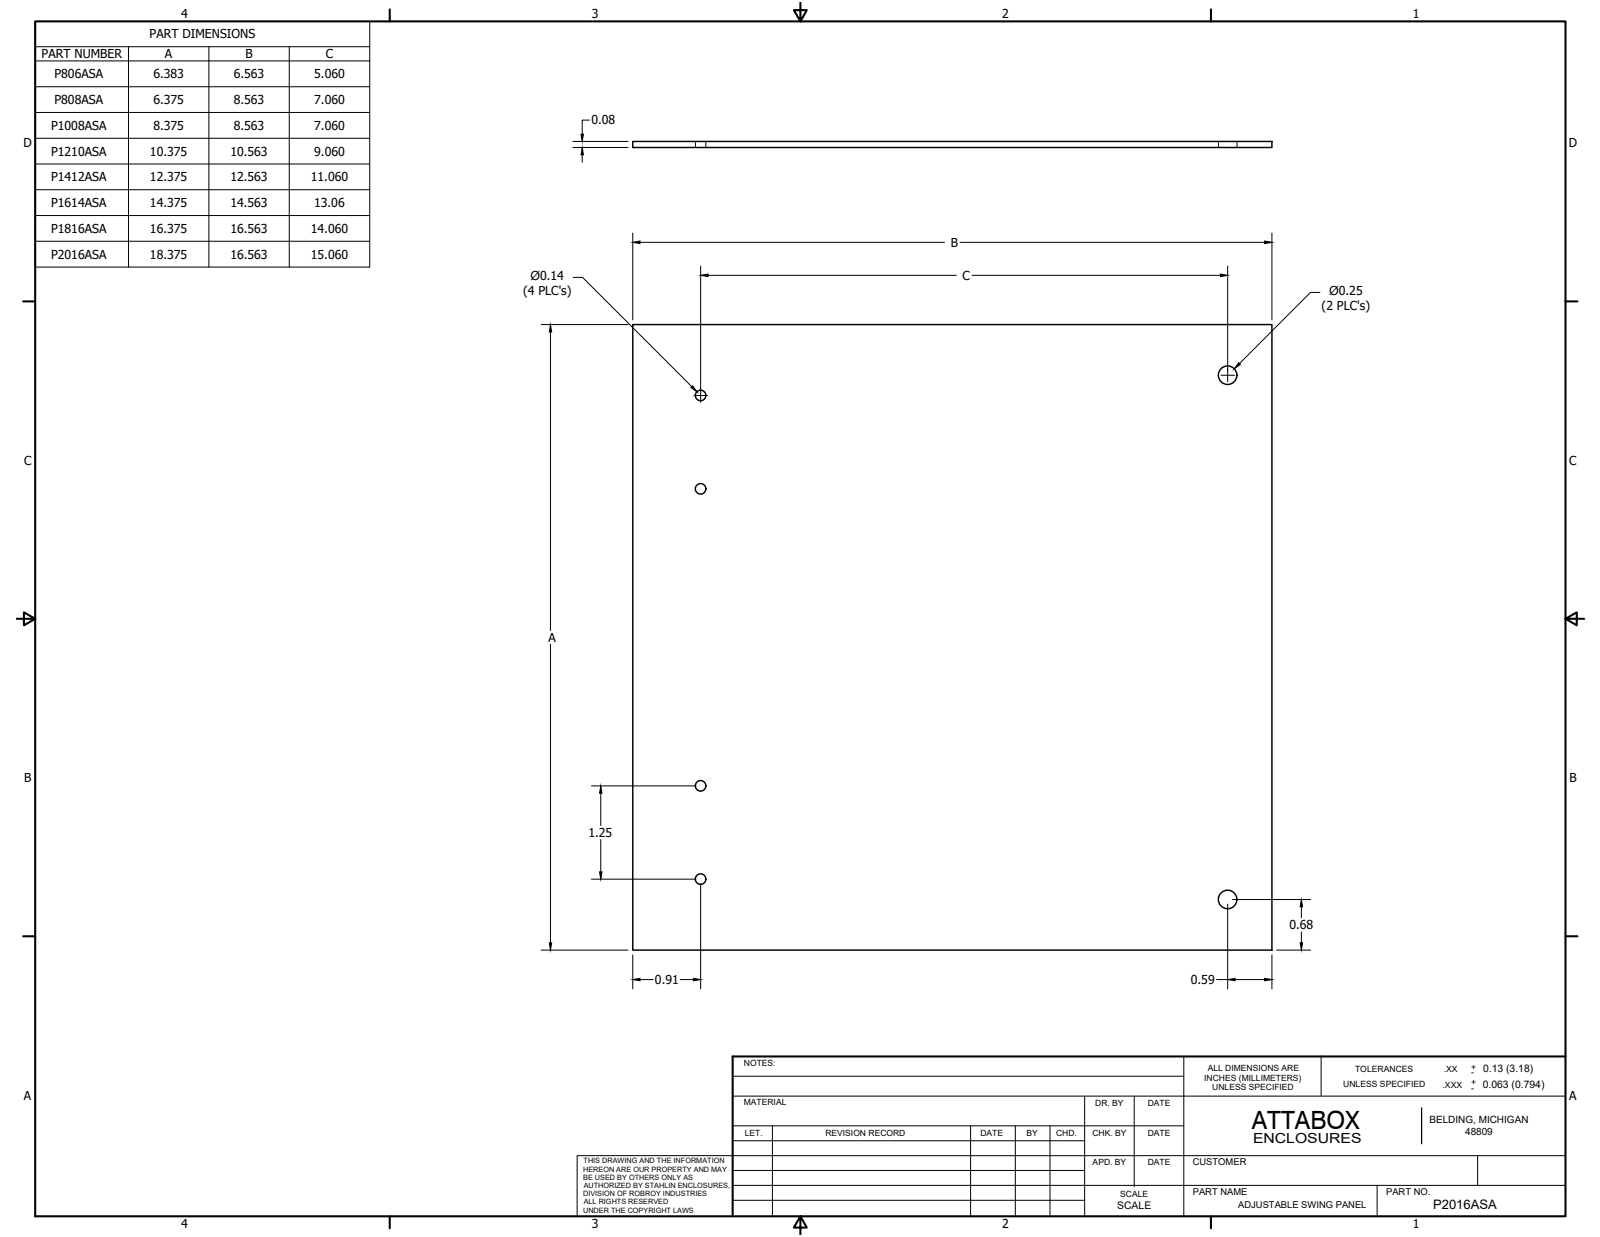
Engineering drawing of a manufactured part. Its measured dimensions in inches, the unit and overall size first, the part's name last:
Units: inches
Overall size (bounding box): 18.375 × 16.563 × 0.08
Round holes (diameter × count): ⌀0.14 ×4, ⌀0.25 ×2
Main face-to-face distances: 0.08, 16.562, 18.375
Hole centre spacings: 1.25, 15.063, 15.137, 15.226, 21.609, 22.523, 13.976, 16.476
Volume: 24.33 in³ · Surface area: 614.2 in²
Bodies: 1 solid, 12 faces (6 planar, 6 cylindrical, 0 other)
Part name (STEP PRODUCT): P2016ASAL
STEP written by: Autodesk Inventor 11 (AUTOMOTIVE_DESIGN)
